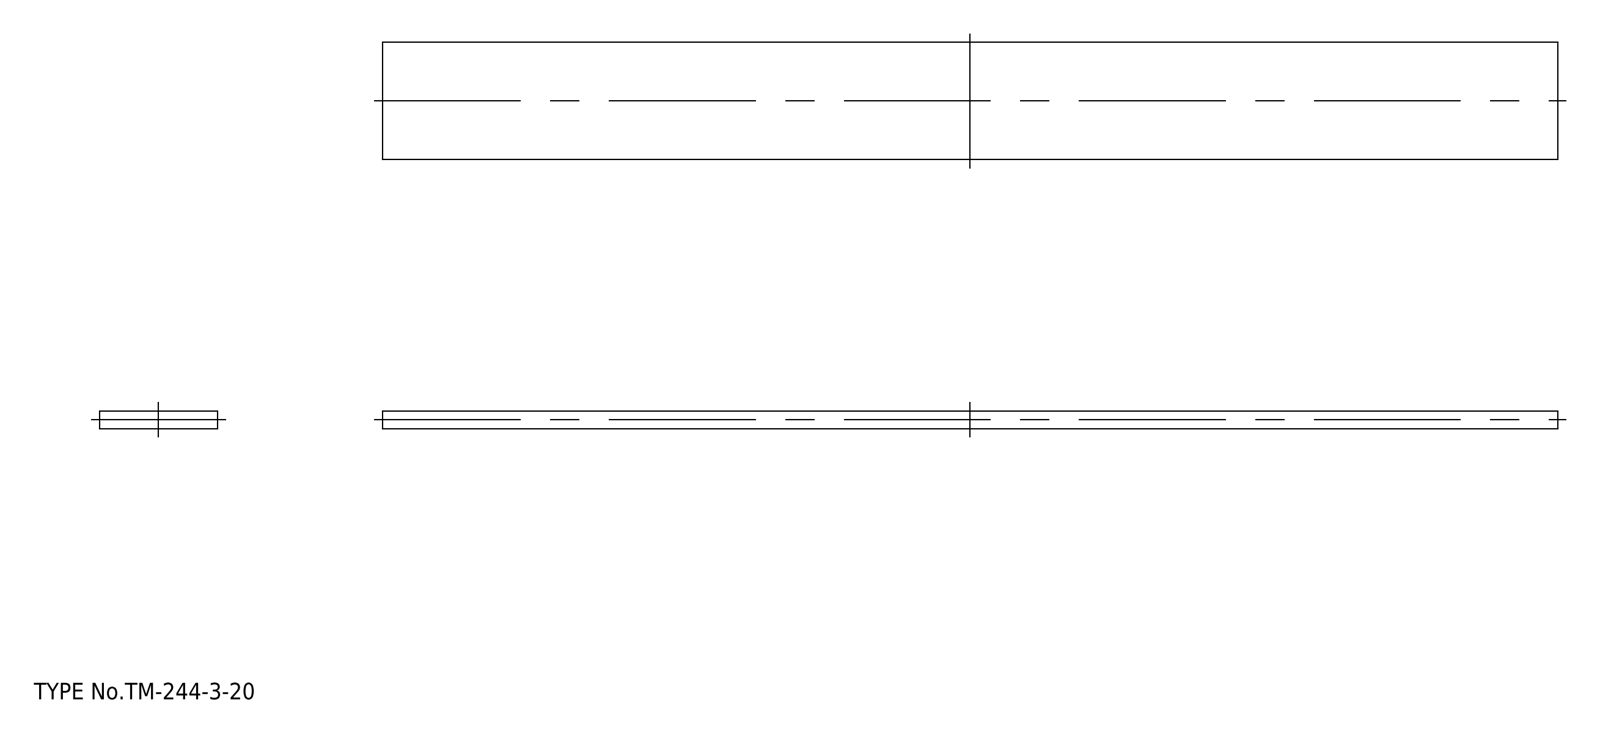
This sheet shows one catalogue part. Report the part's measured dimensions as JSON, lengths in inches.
{"step_written_by": "spGate 18.9.1 (****-****-****-****) (AUTOMOTIVE_DESIGN)", "units": "inches", "bodies": {"solids": 1, "faces": 6, "planar": 6, "cylindrical": 0, "other": 0}, "overall_size": [7.874, 0.787, 0.118], "volume_in3": 0.732, "surface_area_in2": 14.45, "face_to_face_distances": [0.118, 0.787, 7.874]}
